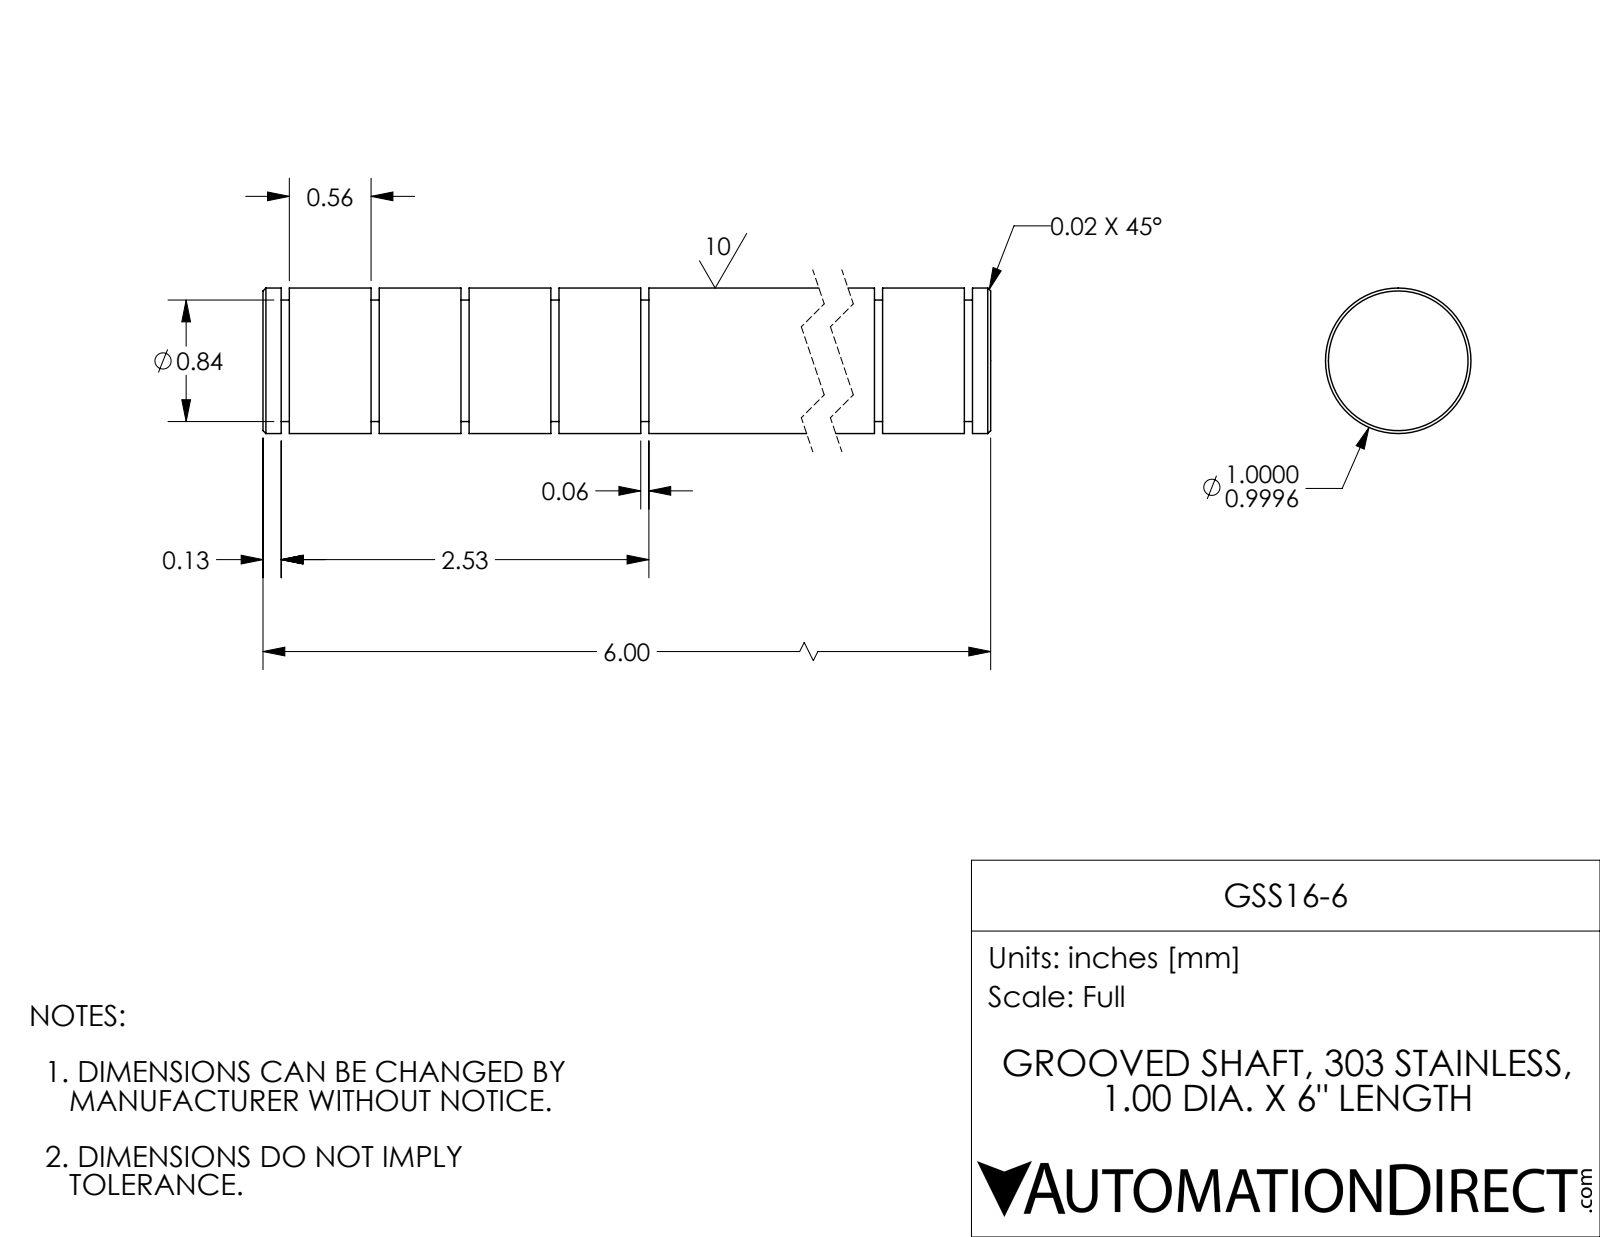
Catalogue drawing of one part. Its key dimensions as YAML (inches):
part_name: "GSS16-6"
step_written_by: "SolidWorks 2017 (AUTOMOTIVE_DESIGN)"
units: inches
bodies: {solids: 1, faces: 50, planar: 16, cylindrical: 30, other: 4}
overall_size: [6, 1, 1]
volume: 4.618
surface_area: 23.47
round_bosses_or_shafts:
  - {diameter: 1, count: 1}
  - {diameter: 0.835, count: 1}
face_to_face_distances: [0.618, 0.056, 0.618, 0.674, 1.236, 6, 3.222, 1.292, 0.562, 5.076]
